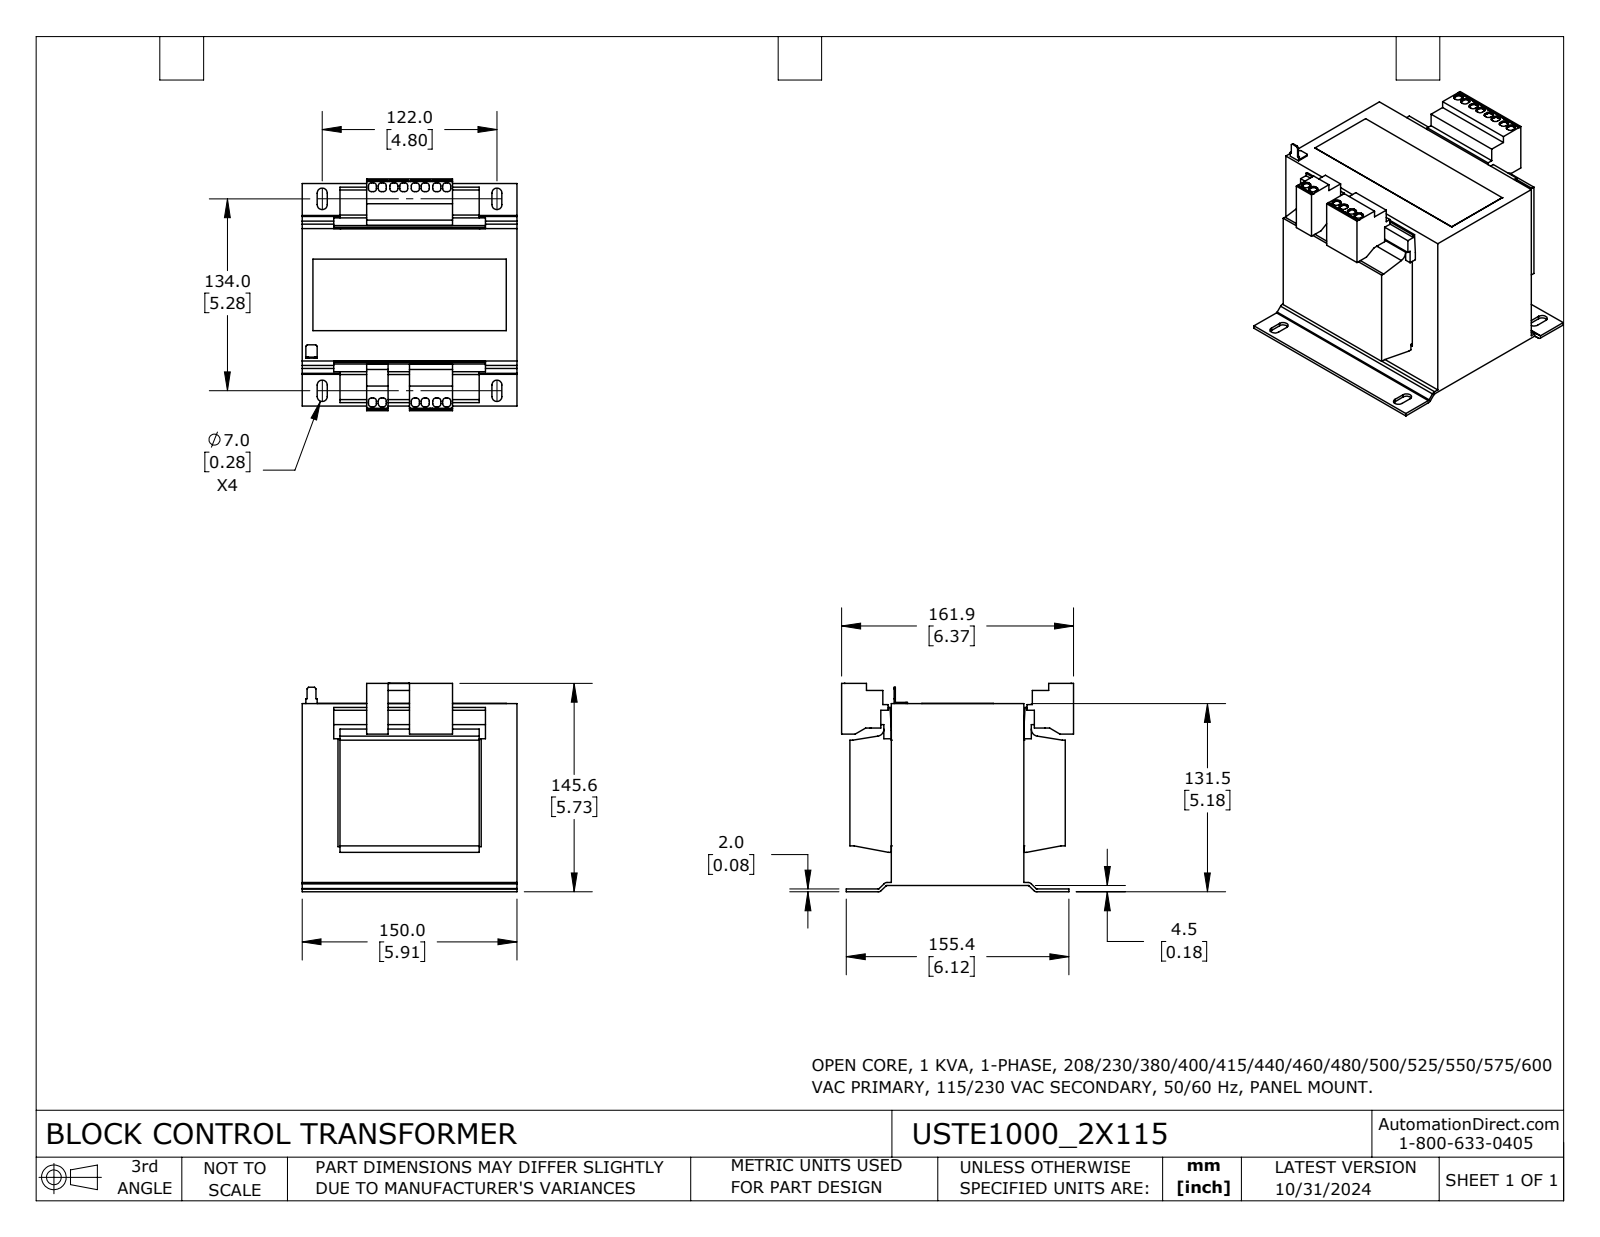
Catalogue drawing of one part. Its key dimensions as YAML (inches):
part_name: "USTE1000_2X115"
step_written_by: "SolidWorks 2023 (CONFIG_CONTROL_DESIGN)"
units: inches
bodies: {solids: 1, faces: 433, planar: 355, cylindrical: 78, other: 0}
overall_size: [6.374, 5.906, 5.731]
volume: 140
surface_area: 329.7
partial_cylinders:
  - {radius: 0.087, count: 56}
  - {radius: 0.138, count: 8}
  - {radius: 0.039, count: 4}
  - {radius: 0.118, count: 4}
  - {radius: 0.197, count: 2}
face_to_face_distances: [1.039, 4.866, 0.984, 4.921, 0.055, 1.14, 4.781, 3.882, 3.937, 5.906]
